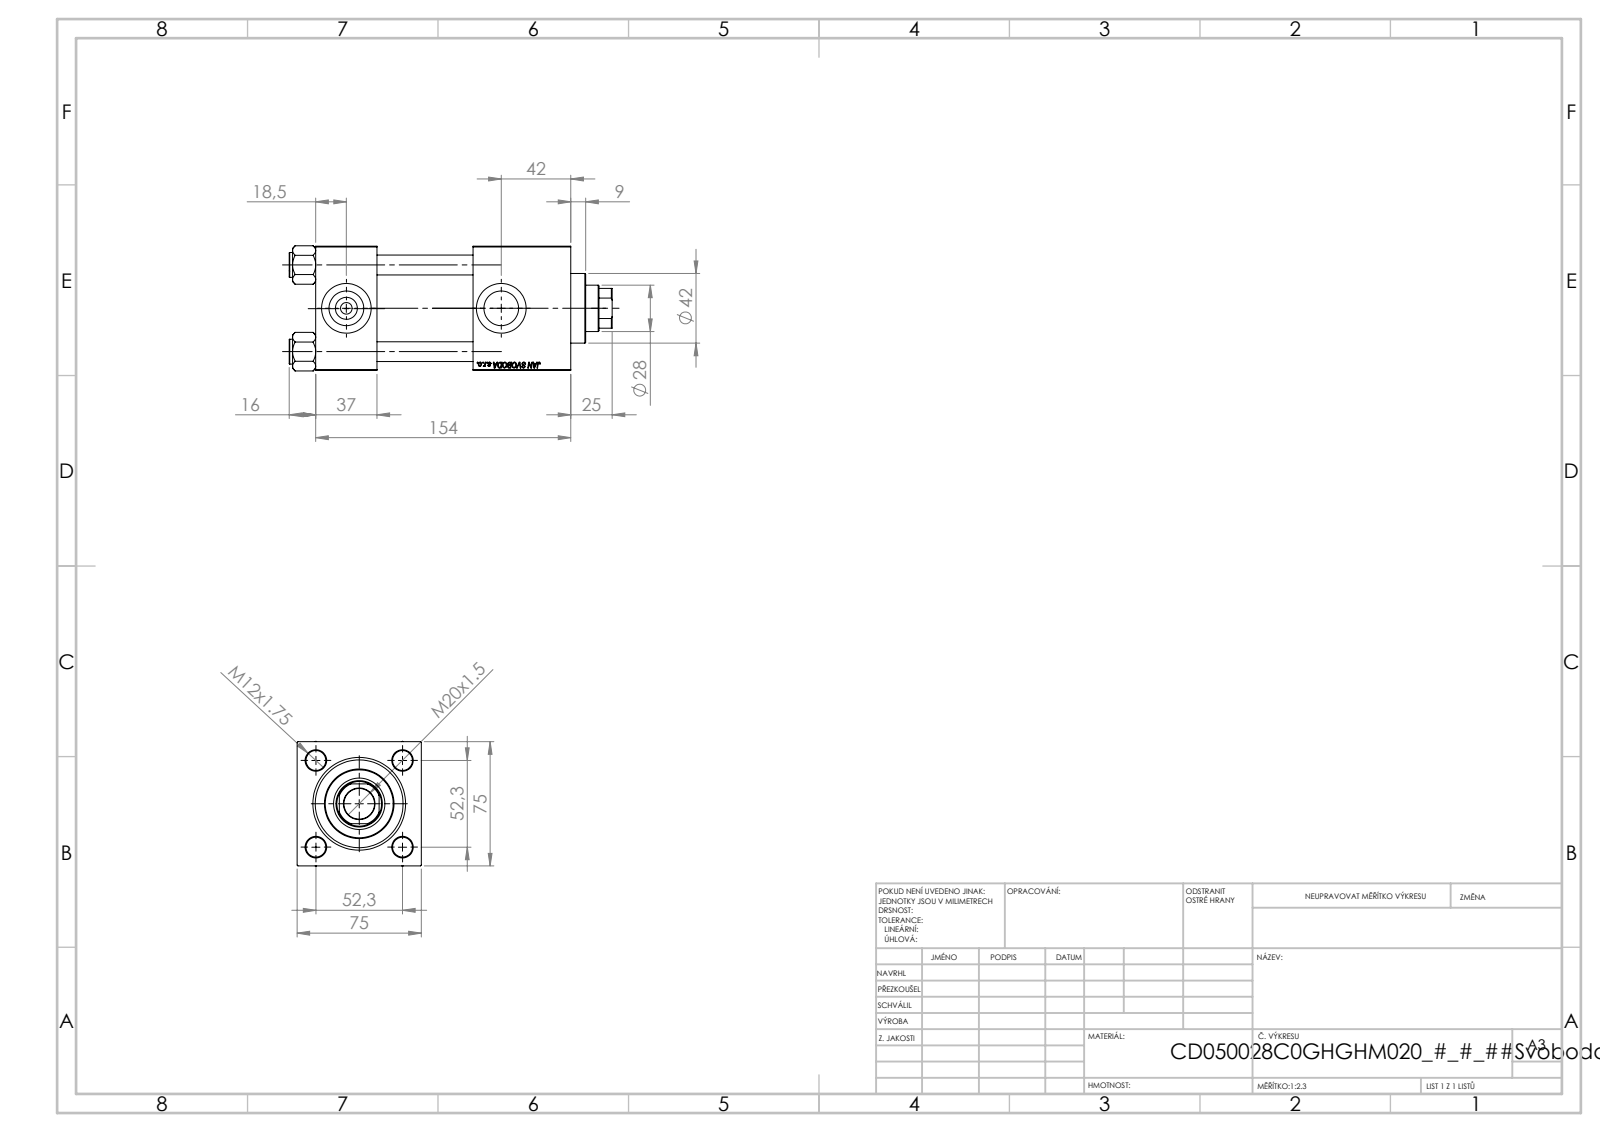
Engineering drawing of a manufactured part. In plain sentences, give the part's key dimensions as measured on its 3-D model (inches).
The part is named "V215CD_Body_C; V215CD_VCP_C; NUT_M5_V215CD_C; V215CD_VC_C (+1 more)". Its 3-D file was written by "SolidWorks 2019 (CONFIG_CONTROL_DESIGN)". It is 11 solids with 1148 faces: 526 planar, 86 cylindrical and 536 other. Overall it measures 7.677 by 2.974 by 2.953 inches. Its volume is 40.83 cubic inches and its surface area 233.9 square inches. Round holes: 4 of diameter 0.472, 2 of diameter 0.276, 2 of diameter 0.825, 2 of diameter 1.181, 1 of diameter 0.728, 1 of diameter 1.102, 1 of diameter 1.22, 1 of diameter 1.614, 1 of diameter 1.969, 1 of diameter 2.087. Round bosses or shafts: 4 of diameter 0.591, 1 of diameter 2.205, 1 of diameter 1.654. Partial cylindrical surfaces (rounded edges, fillets, slot ends): 1 of radius 0.531. The main face-to-face distances are 2.953, 1.457, 6.063, 4.606, 3.74, 2.283, 2.323, 4.933, 3.476, 1.193. The hole center spacings are 1.456, 2.059, 2.912, 3.681.
